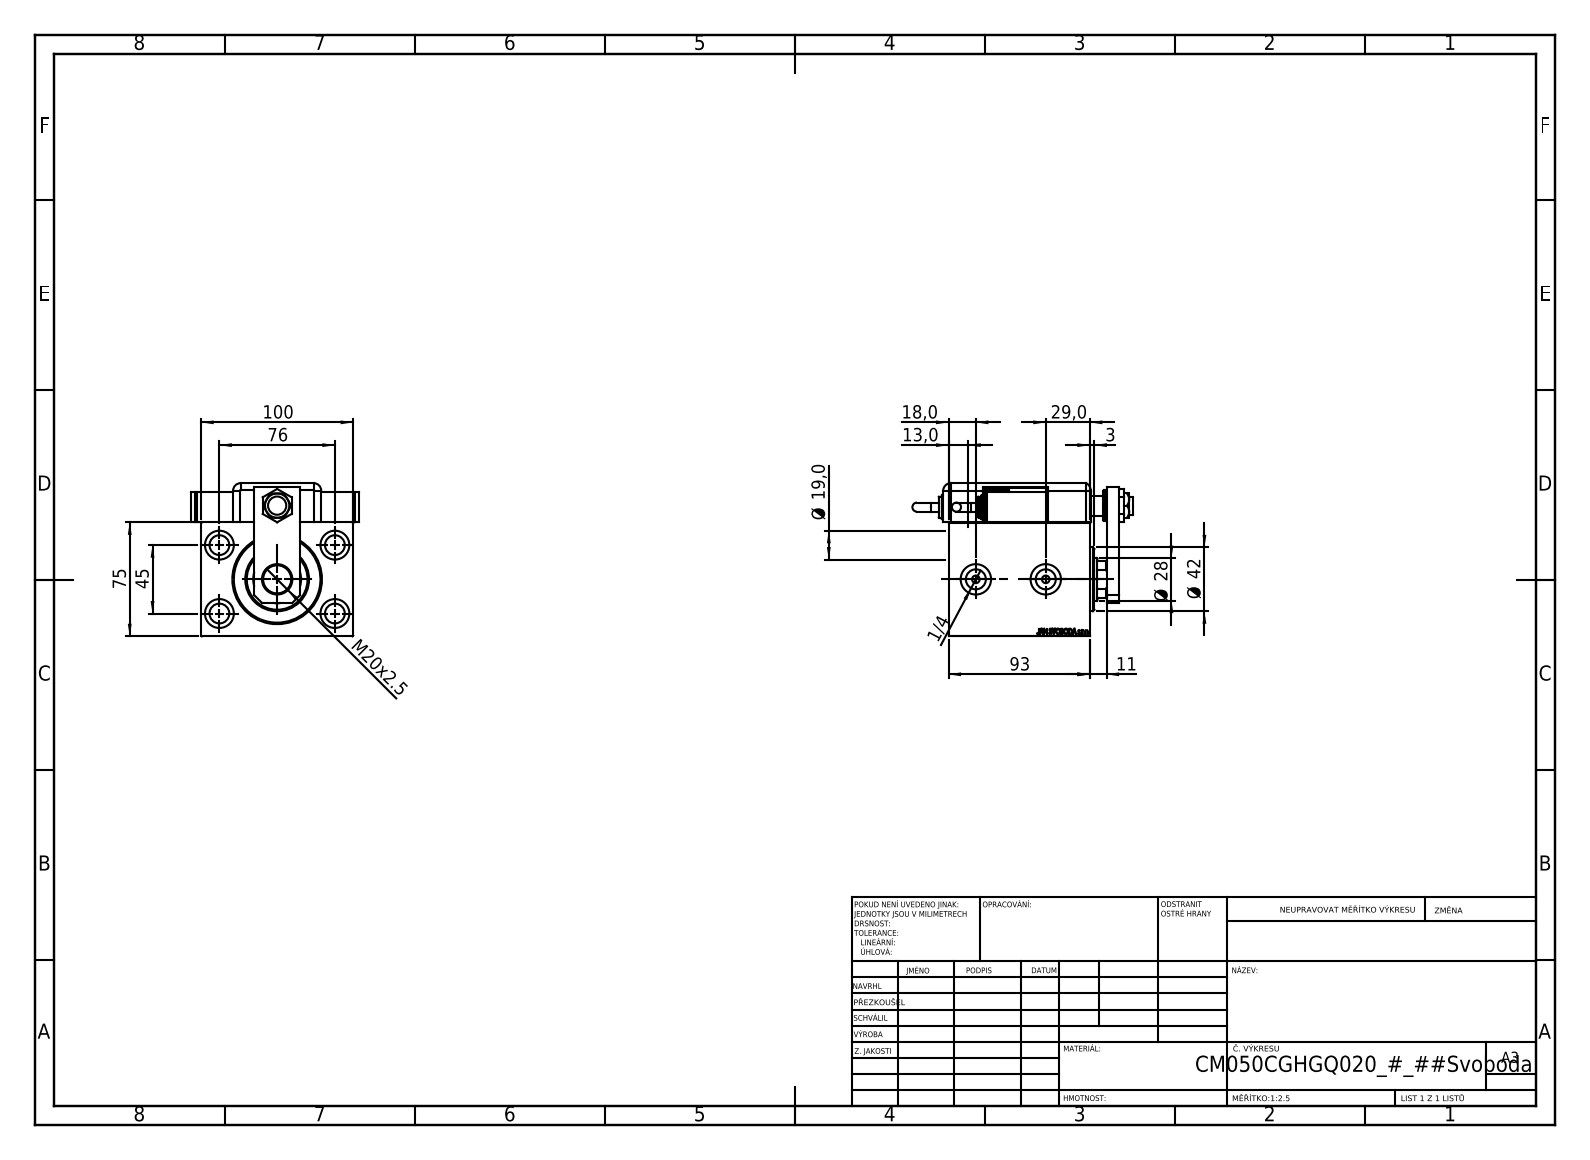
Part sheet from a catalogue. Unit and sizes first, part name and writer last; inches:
Units: inches
Overall size (bounding box): 5.727 × 4.37 × 3.969
Round holes (diameter × count): ⌀0.512 ×5, ⌀0.748 ×4, ⌀0.787 ×3, ⌀0.157 ×2, ⌀0.197 ×2, ⌀0.315 ×2, ⌀0.518 ×2, ⌀0.472 ×1, ⌀0.551 ×1, ⌀0.728 ×1, ⌀1.102 ×1, ⌀1.24 ×1
Round bosses / shafts (diameter × count): ⌀0.787 ×3, ⌀0.63 ×2, ⌀0.551 ×2, ⌀0.236 ×2, ⌀1.654 ×1
Partial cylindrical surfaces — rounded edges, fillets, slot ends (radius × count): R0.197 ×9, R0.394 ×1, R0.531 ×1
Main face-to-face distances: 2.953, 0.118, 3.937, 1.654, 3.661, 2.008, 0.098, 0.315, 1.016, 3.969
Hole centre spacings: 1.739, 1.772, 1.813, 2.992, 3.17, 3.477, 0.787, 1.811
Volume: 46.04 in³ · Surface area: 230.5 in²
Bodies: 13 solids, 1250 faces (616 planar, 117 cylindrical, 517 other)
Part name (STEP PRODUCT): KRYT; V450CM_C_Body; TYC; SWITCH DIM A_G (+7 more)
STEP written by: SolidWorks 2019 (CONFIG_CONTROL_DESIGN)
